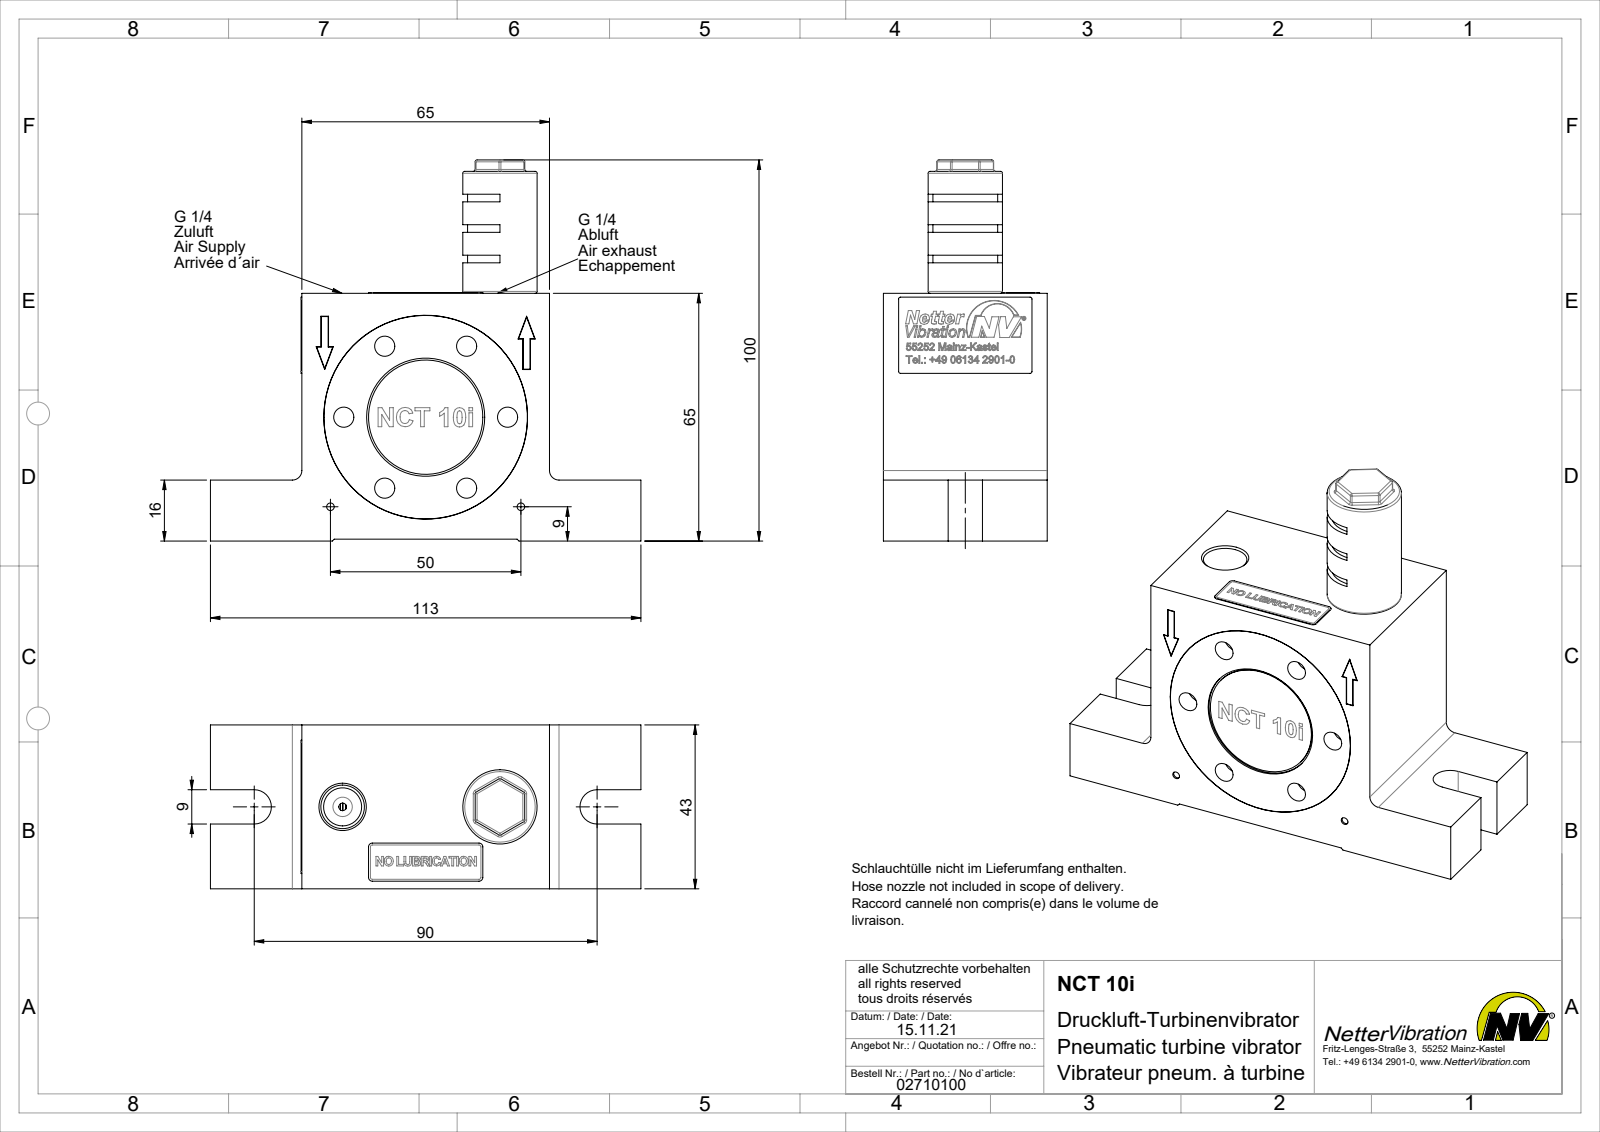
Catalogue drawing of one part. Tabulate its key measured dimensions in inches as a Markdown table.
| quantity | value |
| --- | --- |
| part name | NCT 10i Turbinenvibrator #02710100 |
| STEP written by | SolidWorks 2015 (AUTOMOTIVE_DESIGN) |
| units | inches |
| bodies | 6 solids, 330 faces (206 planar, 71 cylindrical, 53 other) |
| overall size | 4.449 × 3.937 × 1.693 |
| volume | 13.8 in³ |
| surface area | 64.14 in² |
| round holes (diameter × count) | 0.209 × 6, 0.079 × 2, 0.451 × 2, 1.22 × 1, 2.063 × 1 |
| round bosses / shafts (diameter × count) | 2.126 × 1, 2.026 × 1, 1.181 × 1, 0.768 × 1, 0.518 × 1 |
| partial cylindrical surfaces (radius × count) | 0.02 × 22, 0.039 × 4, 0.098 × 2, 0.177 × 2, 0.335 × 1 |
| main face-to-face distances | 2.559, 1.693, 0.02, 0.315, 1.378, 0.157, 1.22, 2.539, 0.472, 0.63 |
| hole center spacings | 0.846, 1.466, 1.693, 0.593, 0.935, 1.351, 1.42, 1.751 |
